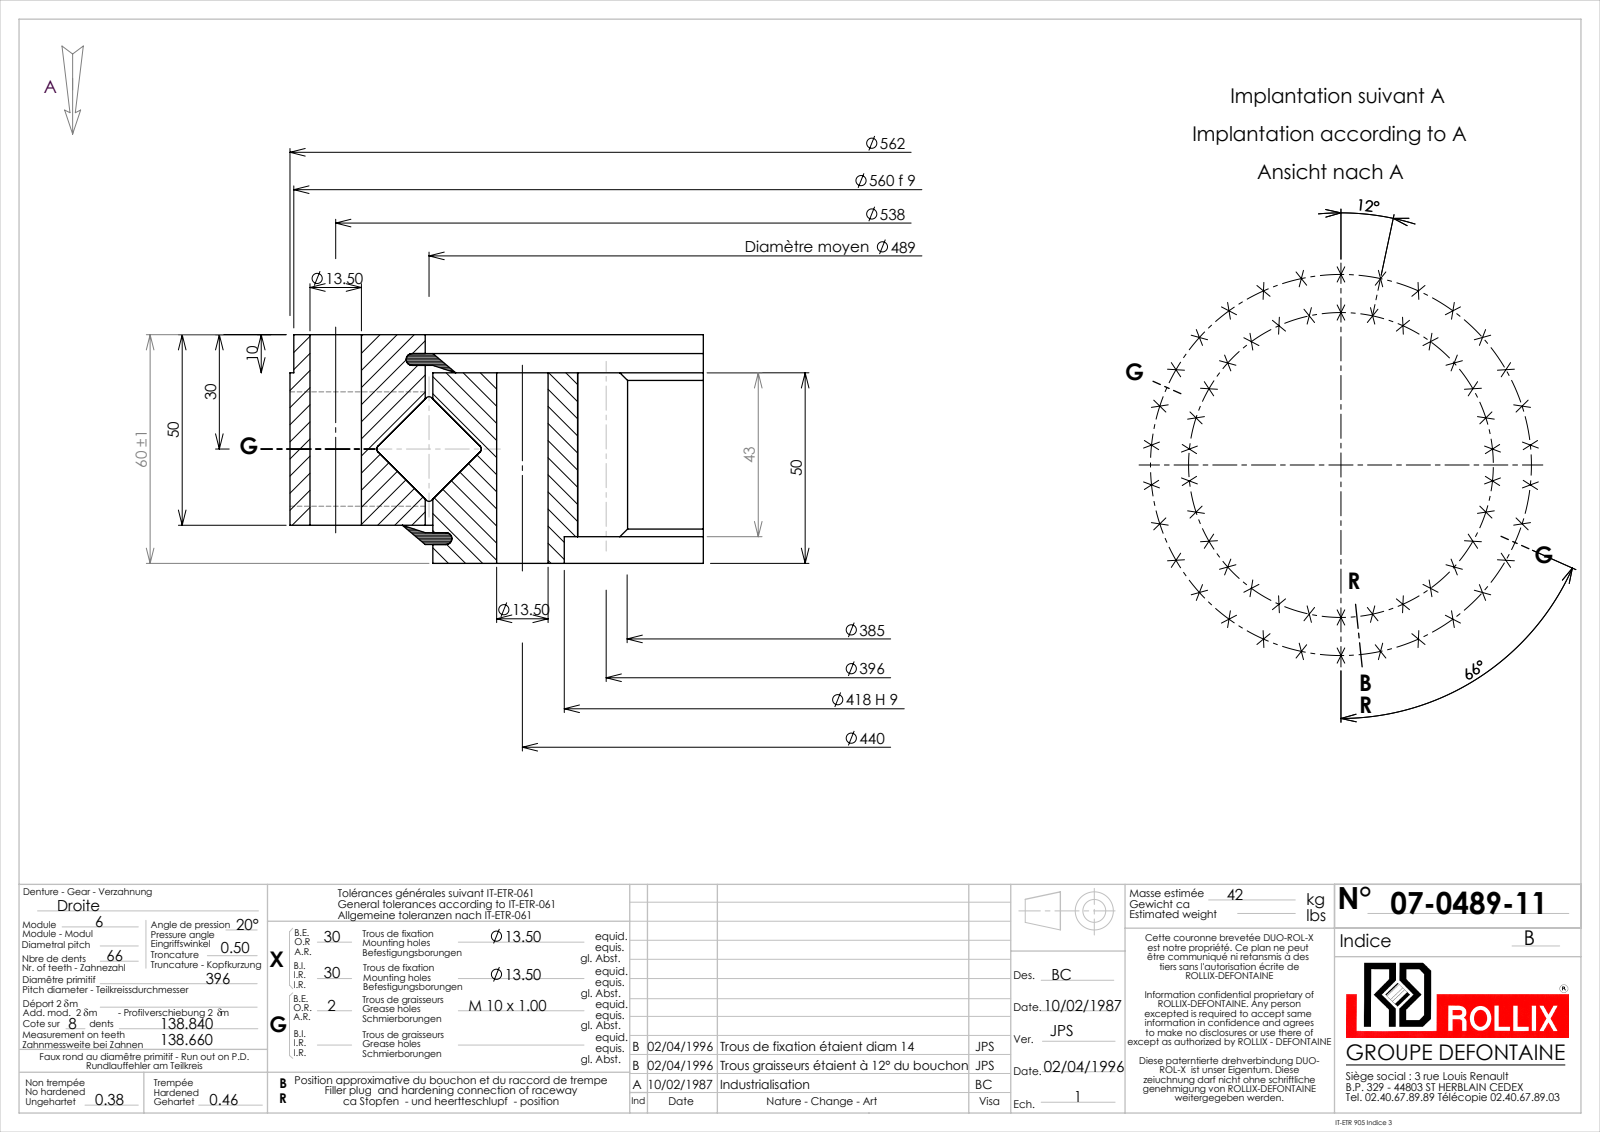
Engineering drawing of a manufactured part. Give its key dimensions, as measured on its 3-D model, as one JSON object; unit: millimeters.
{"part_name": "07-0489-11", "step_written_by": "SolidWorks 2016 (CONFIG_CONTROL_DESIGN)", "units": "millimeters", "bodies": {"solids": 5, "faces": 596, "planar": 148, "cylindrical": 277, "other": 171}, "overall_size": [562, 562, 60], "volume_mm3": 5035000, "surface_area_mm2": 859848, "round_holes": [[13.5, 60], [9, 2], [418, 1], [491, 1]], "round_bosses_or_shafts": [[562, 1], [560, 1], [487, 1], [20, 1]], "partial_cylinders_radius": [[192.5, 1], [205.5, 1]], "face_to_face_distances": [10, 50, 40, 60, 4.95, 55.05, 5.05, 45.05, 8.05, 51.95], "hole_center_spacings": [220, 326.98, 418.46, 430.38, 91.48, 45.99, 294.42, 381.05]}
